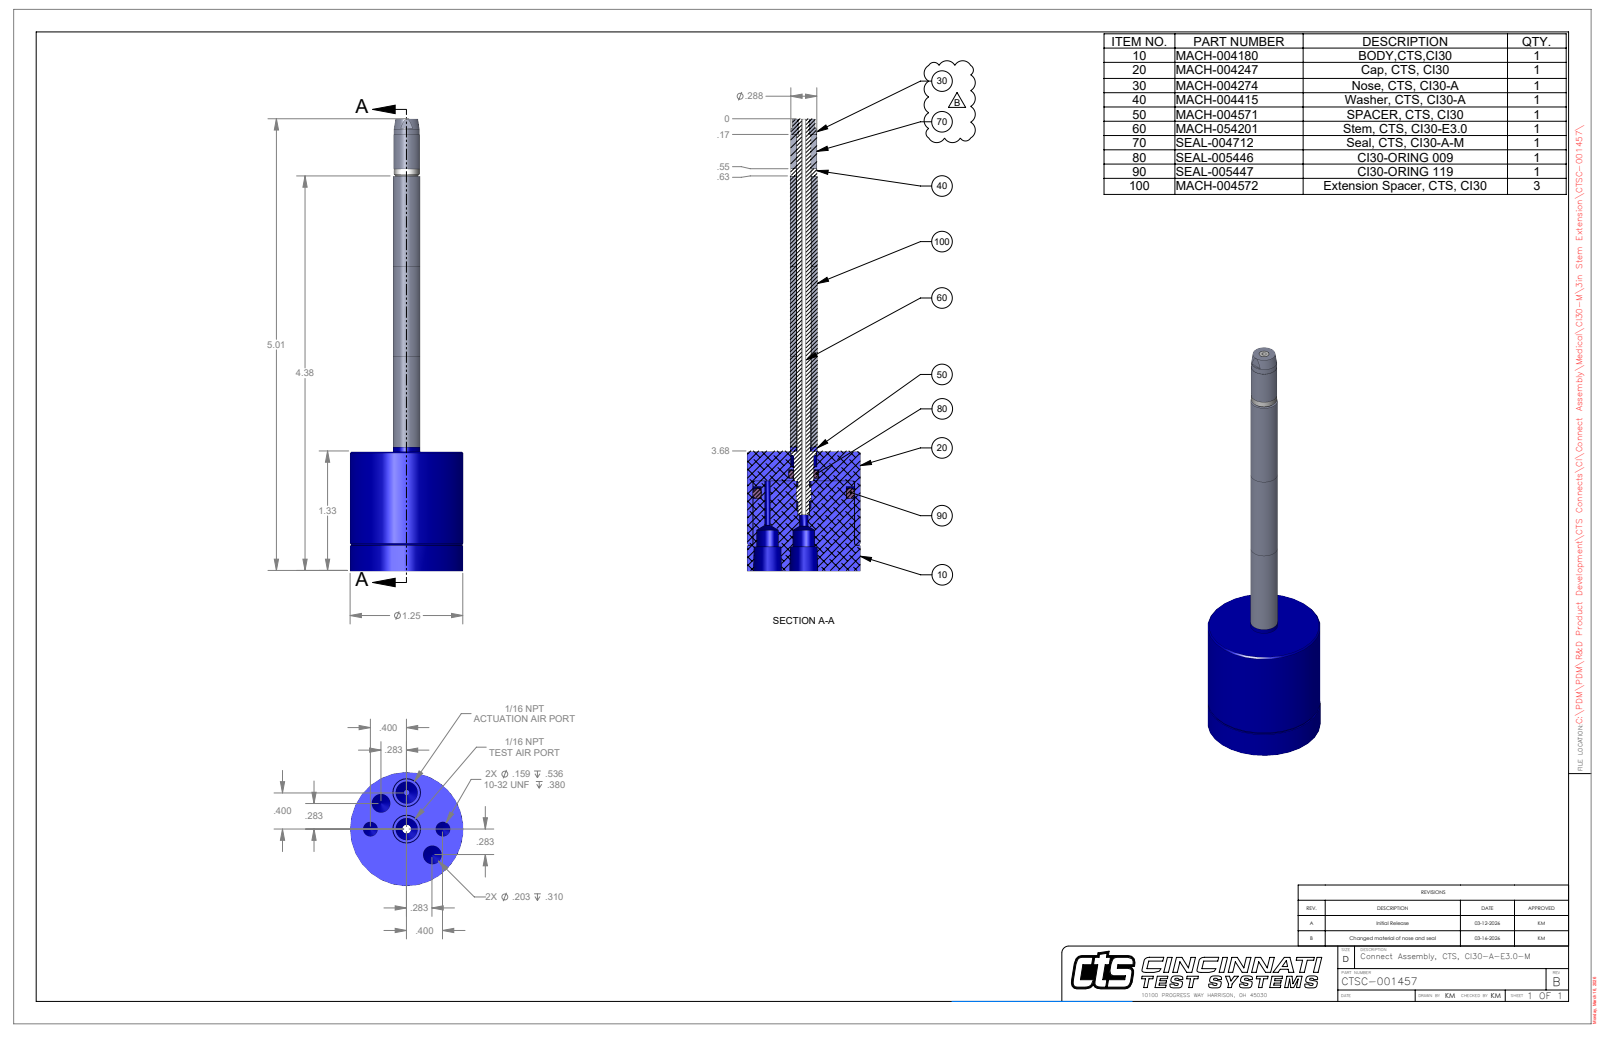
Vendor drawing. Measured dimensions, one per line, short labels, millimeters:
name: CTSC-001457
written by: SolidWorks 2023 (AUTOMOTIVE_DESIGN)
unit: mm
bodies: 8 solids, 85 faces (37 planar, 31 cylindrical, 17 other)
size: 127.23 × 31.75 × 31.75
volume: 28 747 mm³; area: 12 737 mm²
holes: 2× ⌀4.04, 2× ⌀5.16, 2× ⌀6.15, 1× ⌀1.32, 1× ⌀1.57, 1× ⌀2.38, 1× ⌀2.87, 1× ⌀3.94, 1× ⌀4.18, 1× ⌀7.34, 1× ⌀28.58
bosses: 1× ⌀31.75, 1× ⌀28.32, 1× ⌀7.62, 1× ⌀7.32, 1× ⌀7.24, 1× ⌀7.04, 1× ⌀3.94, 1× ⌀3.51
face distances: 33.66, 25.4, 7.28, 26.38, 50.8, 7.37, 26.29, 122.81, 115.53, 115.44
hole spacings: 7.77, 10.16, 18.77, 10.15, 14.37, 20.31, 20.32
